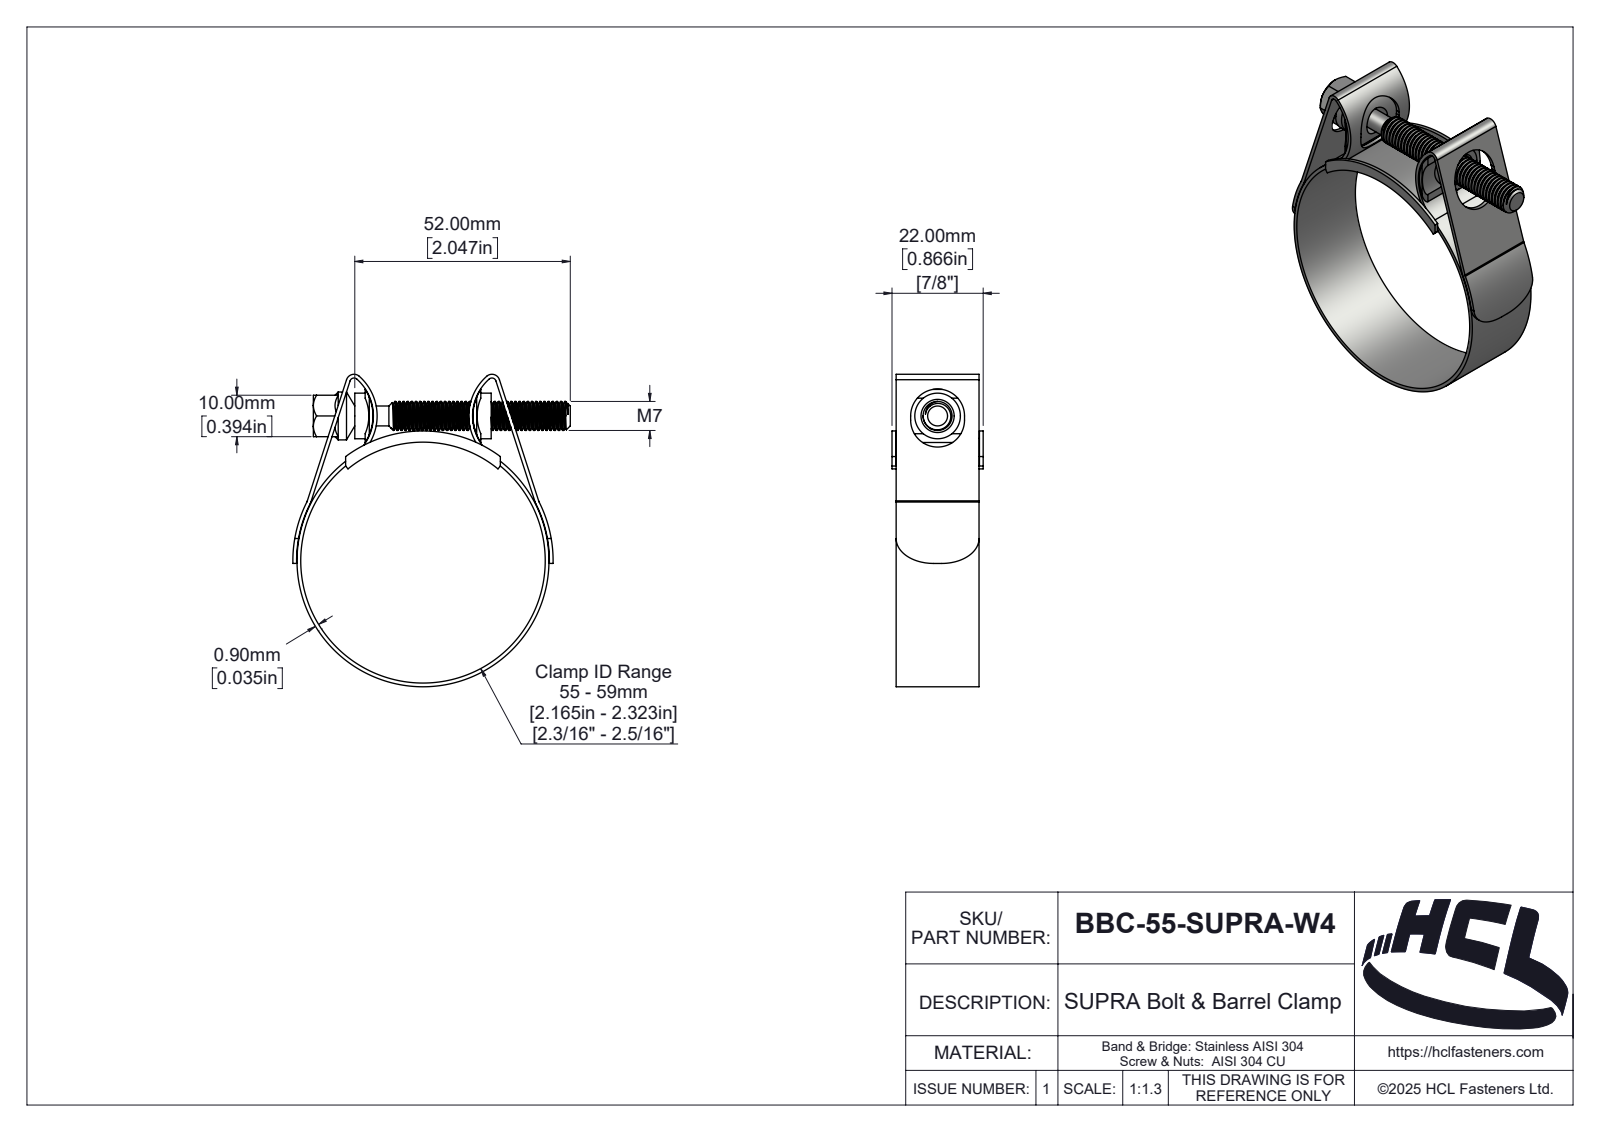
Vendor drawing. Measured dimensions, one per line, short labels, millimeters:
name: BBC-55-SUPRA-W4
written by: SolidWorks 2025 (AUTOMOTIVE_DESIGN)
unit: mm
bodies: 5 solids, 322 faces (46 planar, 197 cylindrical, 79 other)
size: 75.37 × 66.94 × 22
volume: 8 772 mm³; area: 16 709 mm²
holes: 1× ⌀59
bosses: 1× ⌀60.8, 1× ⌀11.55, 1× ⌀11, 1× ⌀7, 1× ⌀4.8
rounds: 6× R1, 2× R1.9, 2× R2, 2× R2.9, 2× R6.5, 2× R10.79, 2× R11.79, 2× R11.88
face distances: 0.9, 20, 1, 21, 21.1, 20.1, 10, 22, 2.5, 30.42
